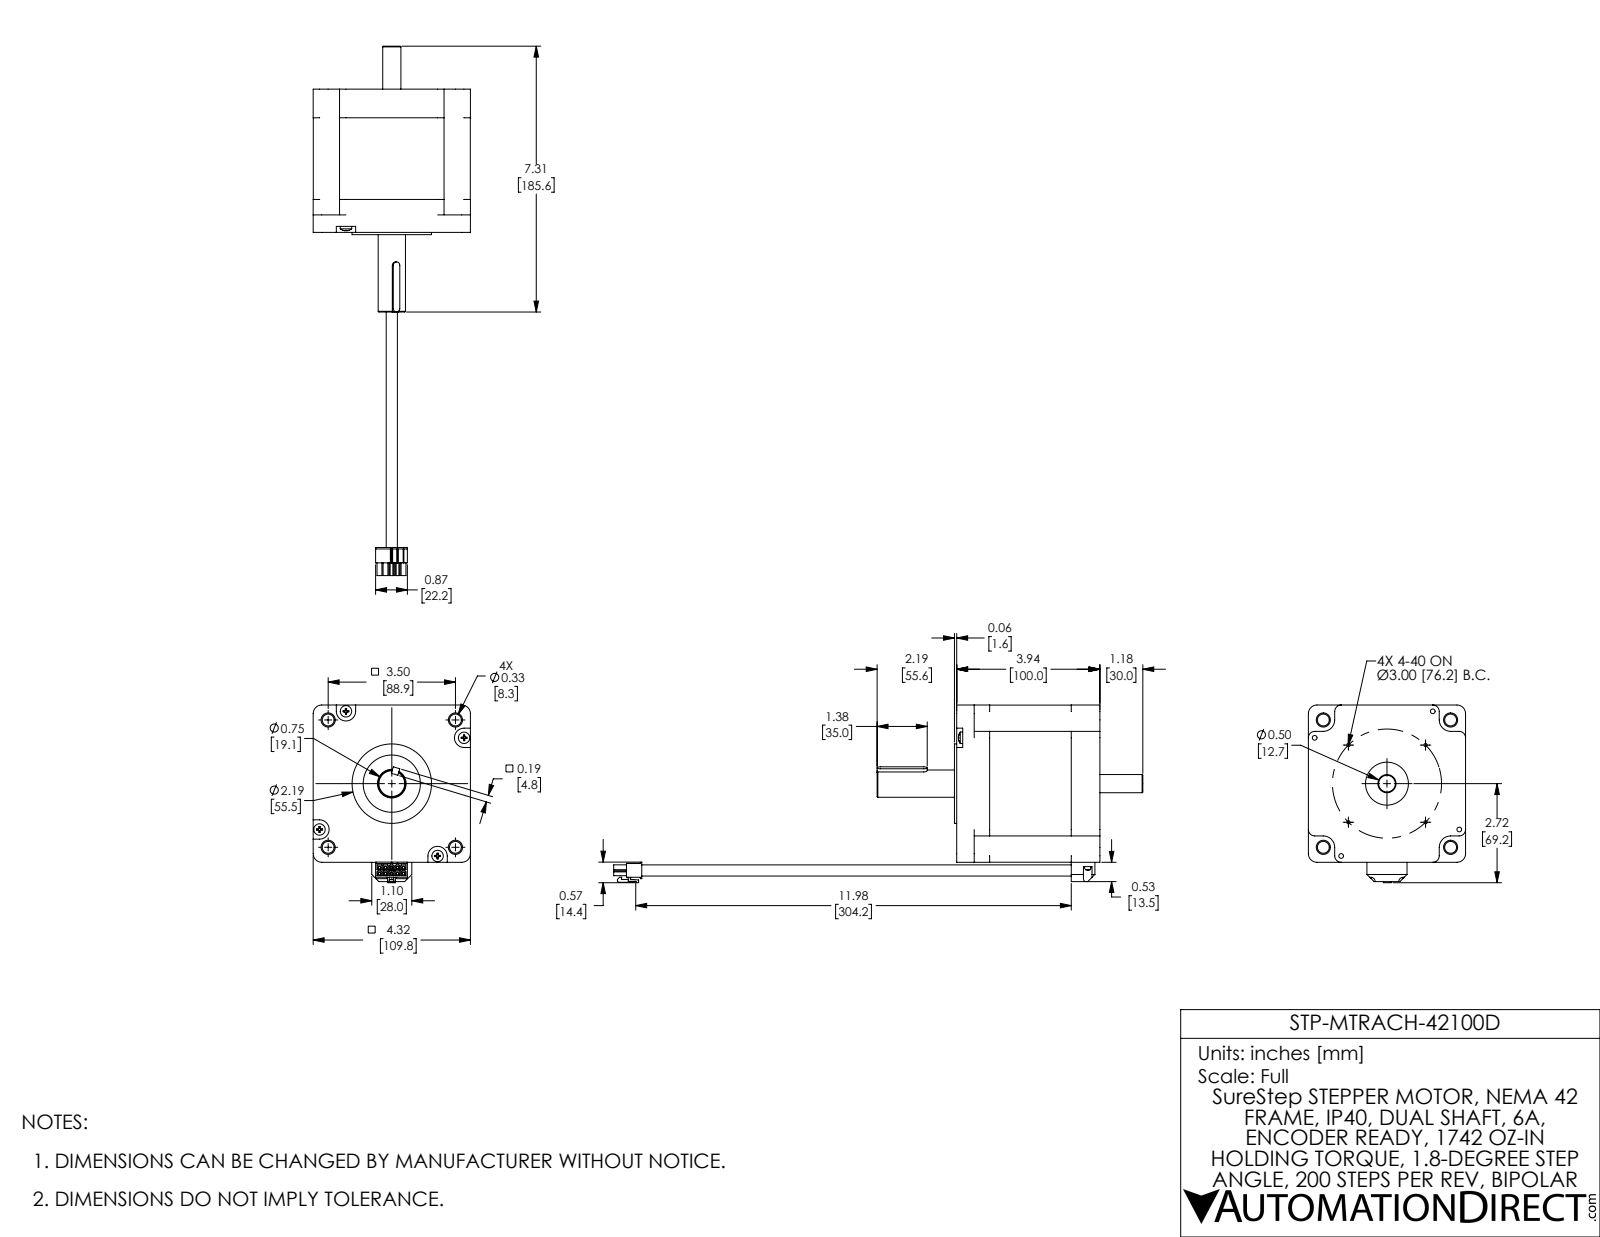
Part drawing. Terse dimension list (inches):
name: STP-MTRAC-42100D
written by: SolidWorks 2017 (AUTOMOTIVE_DESIGN)
unit: in
bodies: 11 solids, 811 faces (595 planar, 183 cylindrical, 33 other)
size: 14.551 × 4.884 × 4.323
volume: 35.79 in³; area: 262.9 in²
holes: 8× ⌀0.177, 6× ⌀0.13, 4× ⌀0.181, 4× ⌀0.327, 1× ⌀1.181, 1× ⌀1.378, 1× ⌀1.575, 1× ⌀2.047, 1× ⌀3.543, 1× ⌀3.976
bosses: 4× ⌀0.315, 4× ⌀0.157, 2× ⌀0.177, 1× ⌀2.579, 1× ⌀2.559, 1× ⌀2.186, 1× ⌀1, 1× ⌀0.787
rounds: 22× R0.012, 16× R0.177, 6× R0.01, 4× R0.236, 4× R0.266, 4× R0.315, 2× R0.094, 2× R0.118
face distances: 4.321, 3.937, 0.669, 2.854, 4.319, 0.787, 3.15, 3.031, 2.244, 0.906
hole spacings: 0.545, 2.354, 3.019, 3.329, 3.77, 4.799, 1.03, 2.475
